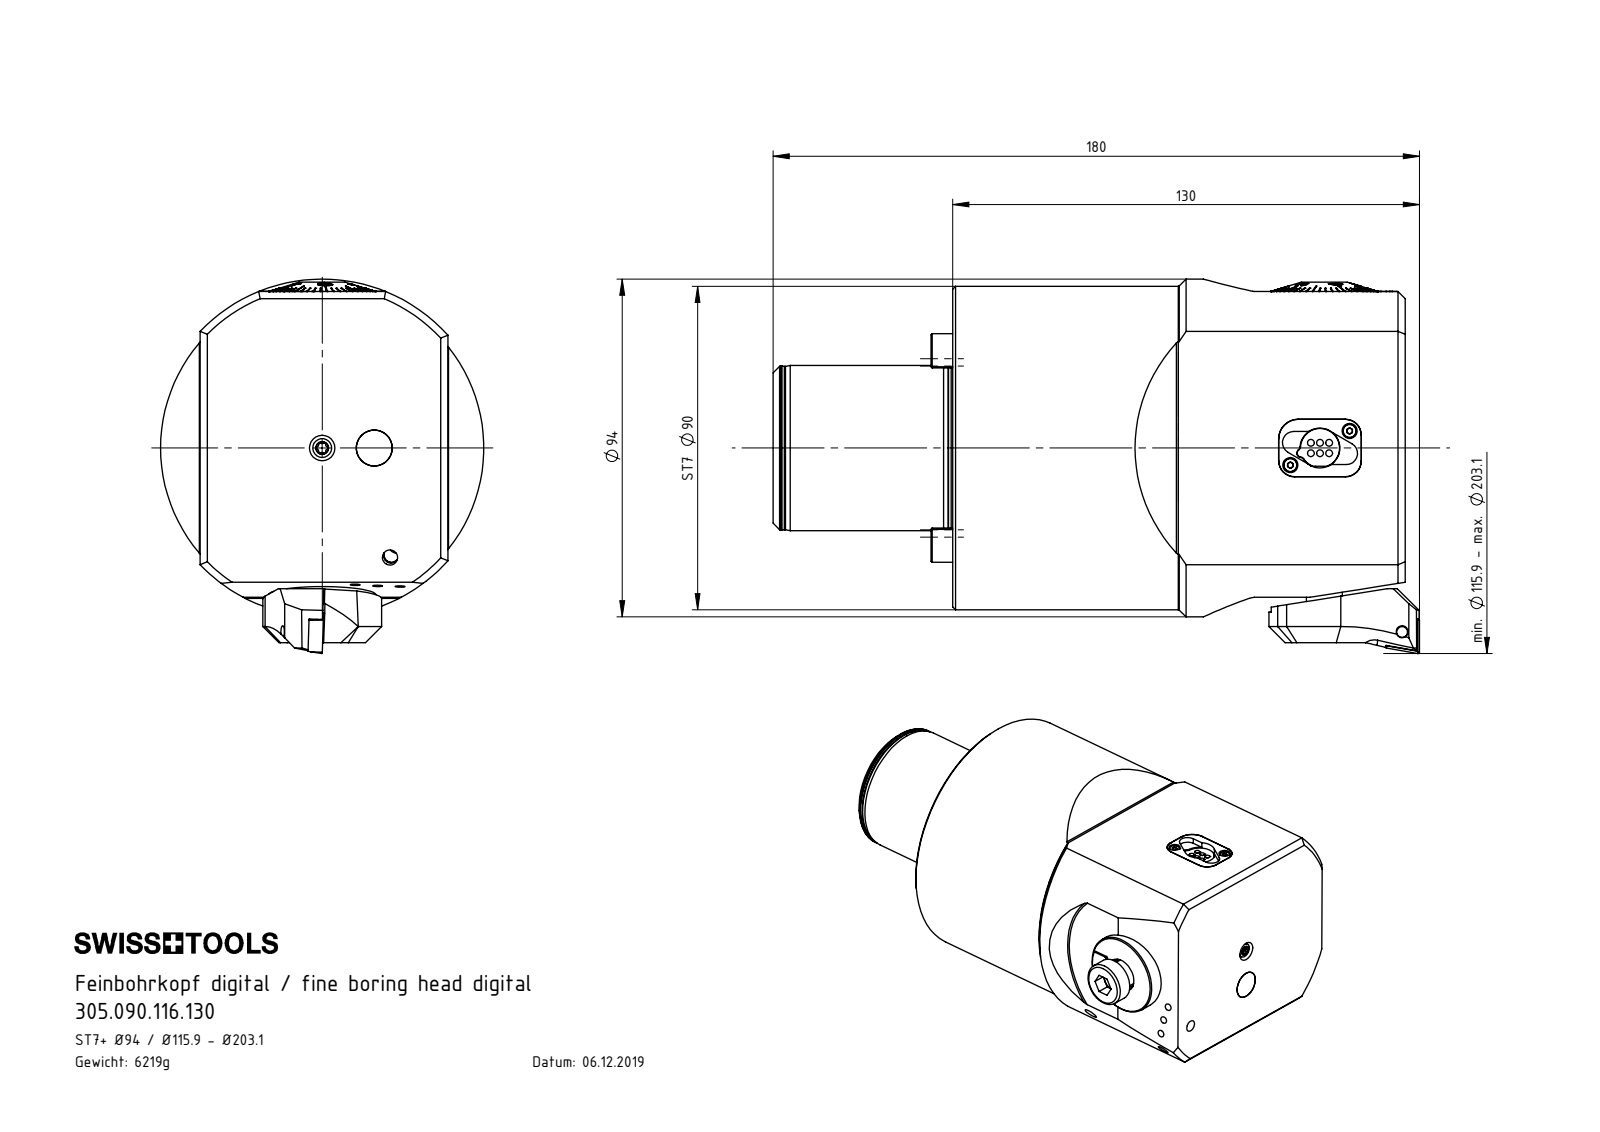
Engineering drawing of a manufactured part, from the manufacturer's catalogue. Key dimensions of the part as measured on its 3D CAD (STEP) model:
Part name (STEP PRODUCT): F94-BG1.DA3.030; WCB-ER2.001.009_A; ST7-F94.DA2.130; F55-BG1.012.012_A (+8 more)
STEP written by: SolidWorks 2017 (CONFIG_CONTROL_DESIGN)
Units: millimetres
Bodies: 30 solids, 1235 faces (486 planar, 303 cylindrical, 446 other)
Overall size (bounding box): 180 × 104.6 × 90
Volume: 769 126 mm³ · Surface area: 110 878 mm²
Round holes (diameter × count): ⌀3.3 ×9, ⌀4.2 ×3, ⌀1.6 ×2, ⌀2.2 ×2, ⌀6 ×2, ⌀8.5 ×2, ⌀10.2 ×2, ⌀13 ×2, ⌀13.5 ×2, ⌀22 ×2, ⌀4.4 ×1, ⌀5 ×1
Round bosses / shafts (diameter × count): ⌀1.9 ×6, ⌀10 ×2, ⌀5.25 ×2, ⌀4 ×2, ⌀3.8 ×2, ⌀2 ×2, ⌀90 ×1, ⌀46 ×1
Partial cylindrical surfaces — rounded edges, fillets, slot ends (radius × count): R0.34 ×12, R0.59 ×12, R0.5 ×8, R1.2 ×8, R1.1 ×6, R4.5 ×4, R3.2 ×3, R4.4 ×3
Main face-to-face distances: 69, 126, 81.6, 88.1, 6.5, 50, 176, 2.5, 3.7, 4
Hole centre spacings: 35, 9.52, 17.65, 19.12, 28, 31.53, 60.88, 5.72
